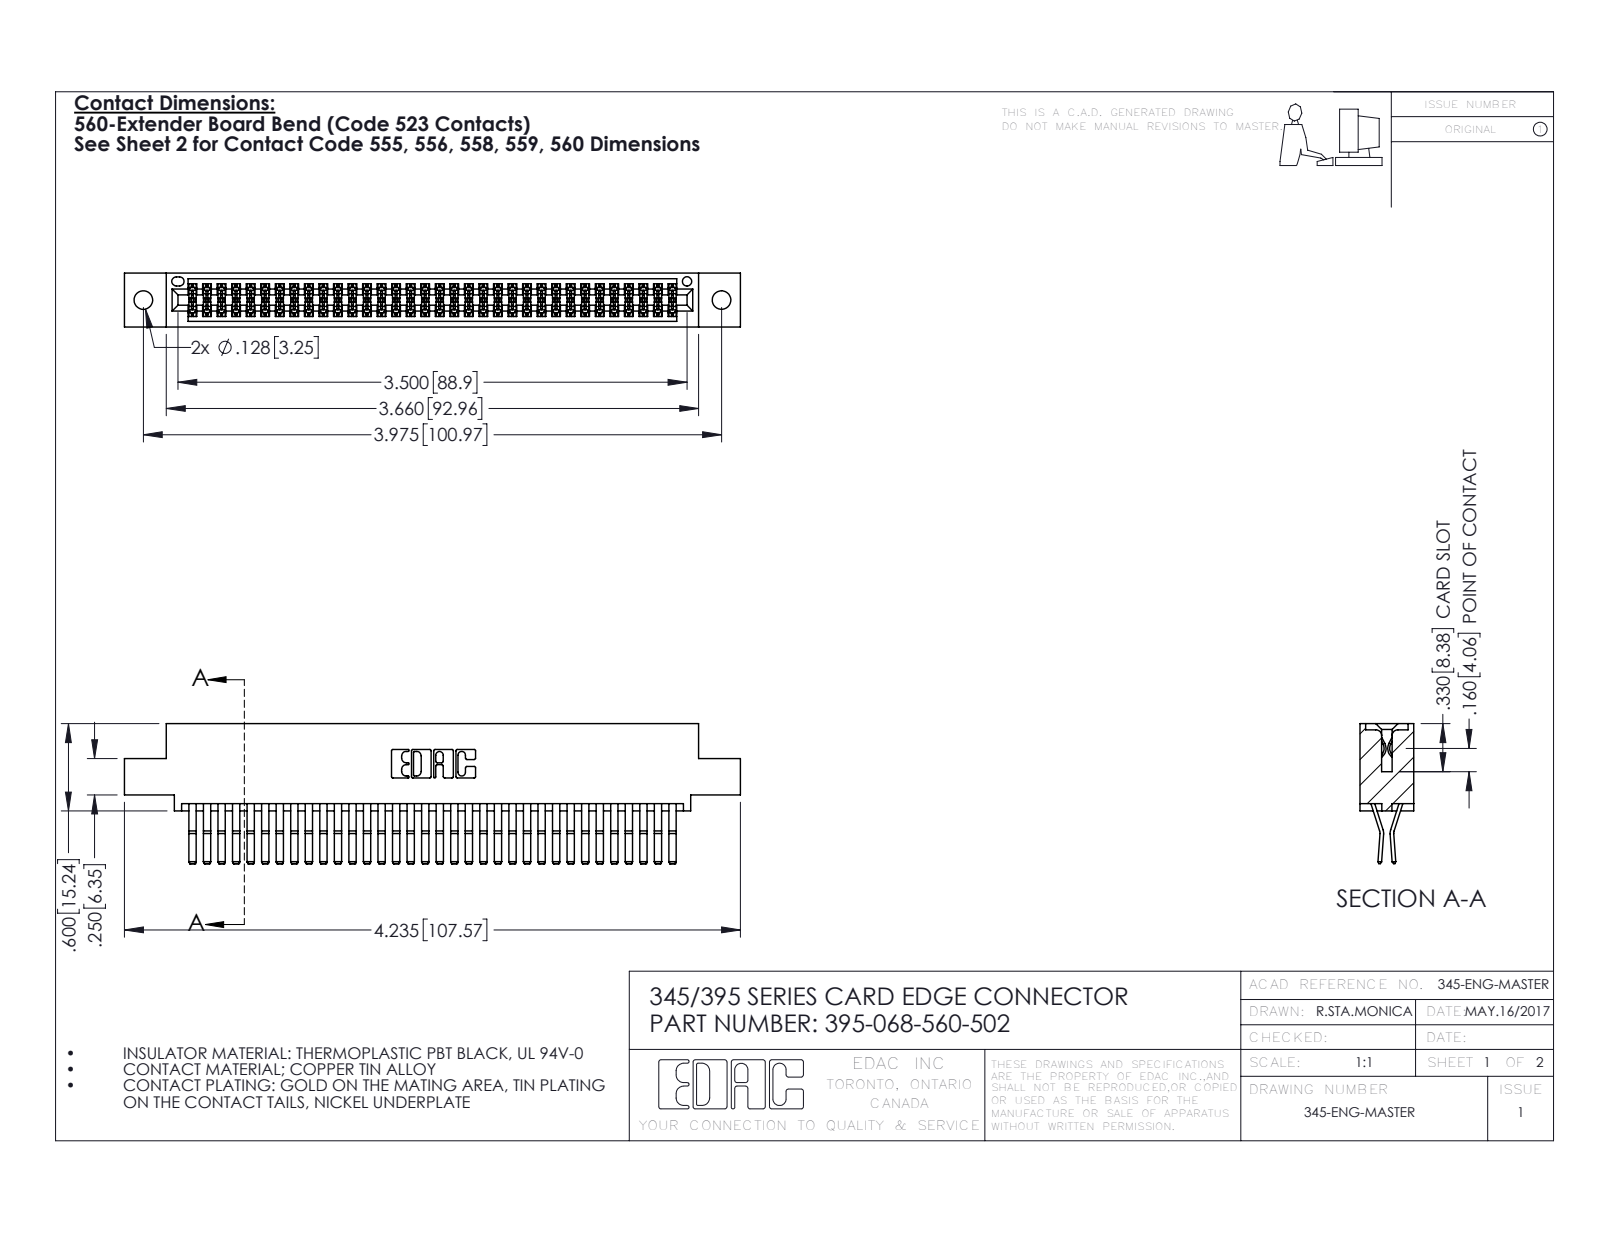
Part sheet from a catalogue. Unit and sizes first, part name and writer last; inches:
Units: inches
Overall size (bounding box): 4.235 × 0.962 × 0.37
Round holes (diameter × count): ⌀0.128 ×2, ⌀0.064 ×1
Partial cylindrical surfaces — rounded edges, fillets, slot ends (radius × count): R0.006 ×102, R0.01 ×22, R0.007 ×6, R0.031 ×6, R0.026 ×3, R0.01 ×2, R0.014 ×2, R0.019 ×2
Main face-to-face distances: 0.025, 0.298, 0.072, 0.37, 0.2, 0.098, 0.272, 0.225, 0.175, 0.149
Hole centre spacings: 0.27, 3.74, 3.975
Volume: 0.654 in³ · Surface area: 25.8 in²
Bodies: 69 solids, 3666 faces (2328 planar, 1338 cylindrical, 0 other)
Part name (STEP PRODUCT): 395-068-560-502; 345 Part_0.110 Offset - 0.128 Dia; 345-292-001_560 Tail
STEP written by: SolidWorks 2016 (CONFIG_CONTROL_DESIGN)
